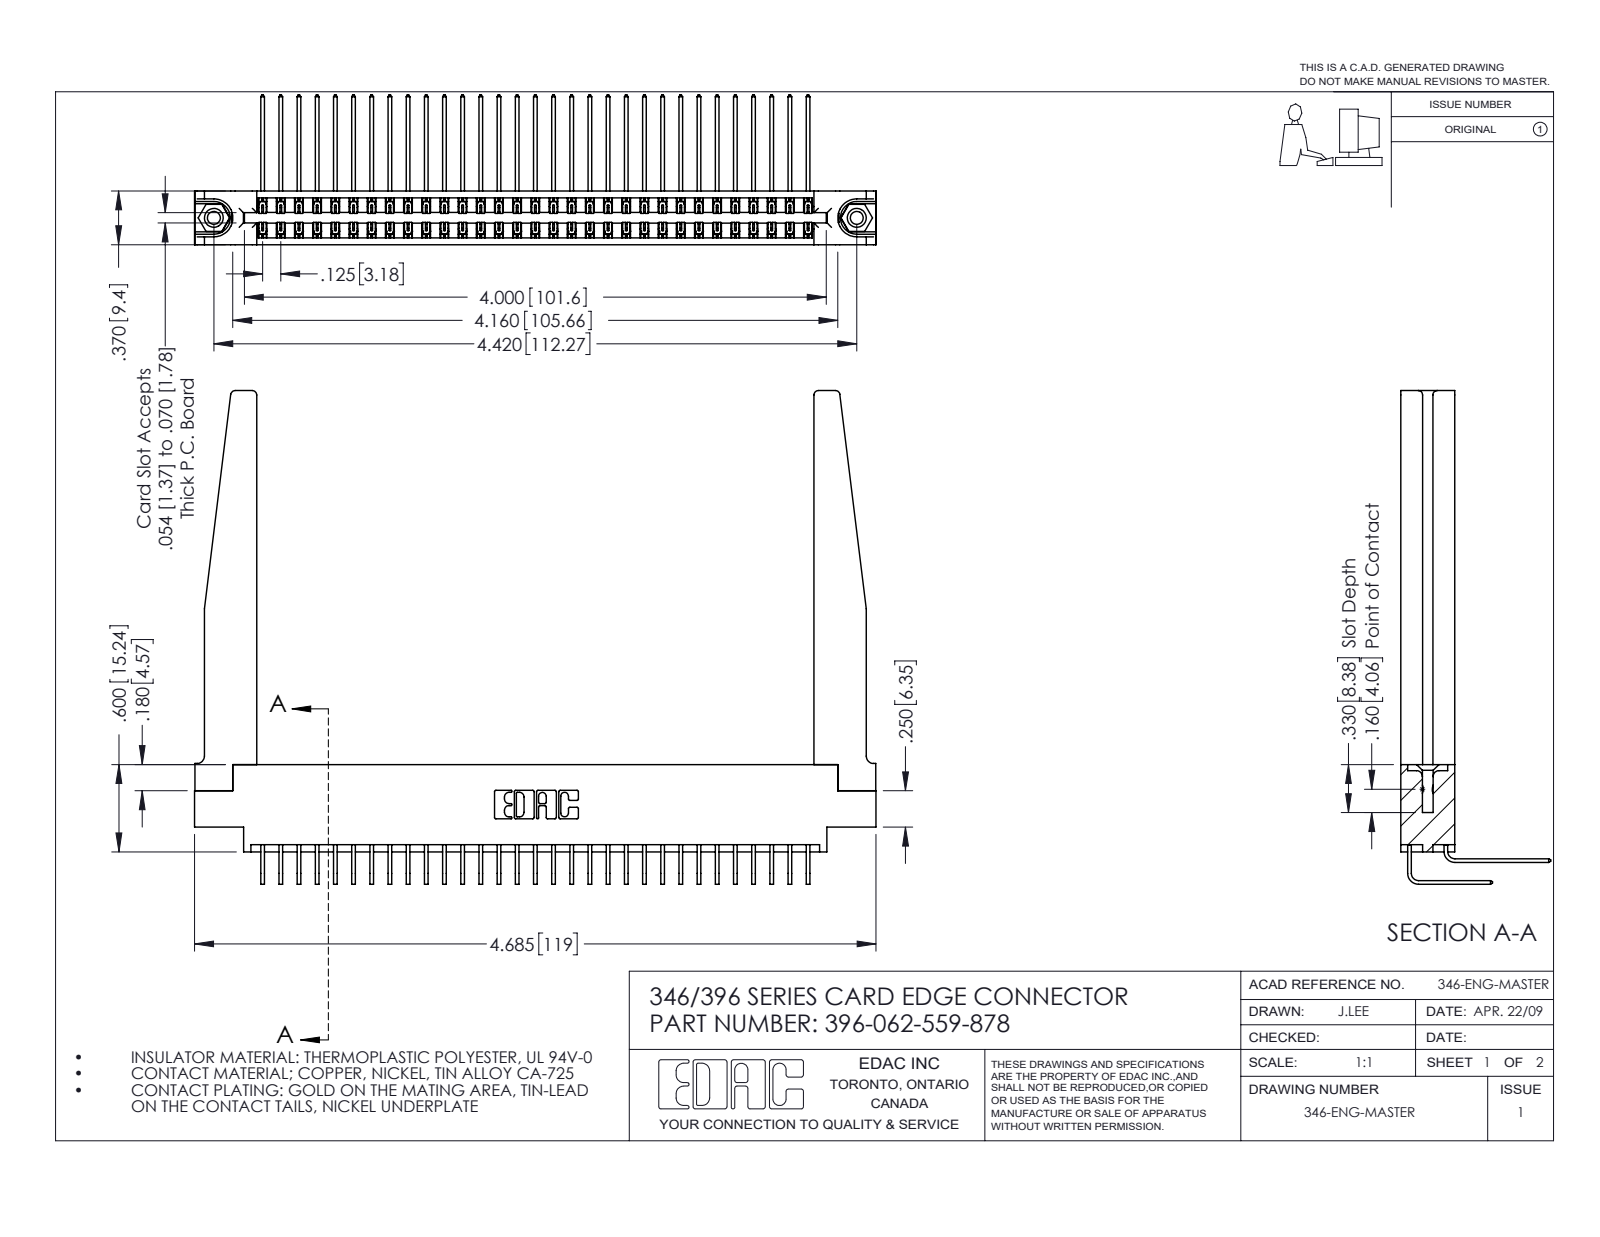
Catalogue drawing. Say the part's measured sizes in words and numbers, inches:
The part is named "345-292-001_559 Tail - 2; 396-062-559-878; 346-220-078_345-220-078; 346 Part_0.170 Offset - 0.156 Dia-TH (+2 more)". Its 3-D file was written by "SolidWorks 2016 (CONFIG_CONTROL_DESIGN)". It is 67 solids with 3708 faces: 2516 planar, 1140 cylindrical and 52 other. Overall it measures 4.685 by 3.393 by 1.03 inches. Its volume is 1.137 cubic inches and its surface area 37.78 square inches. Round holes: 2 of diameter 0.089, 2 of diameter 0.125, 2 of diameter 0.156, 1 of diameter 0.064. Round bosses or shafts: 2 of diameter 0.155. Partial cylindrical surfaces (rounded edges, fillets, slot ends): 93 of radius 0.006, 22 of radius 0.01, 8 of radius 0.03, 6 of radius 0.007, 6 of radius 0.031, 4 of radius 0.05, 3 of radius 0.026, 2 of radius 0.014. The main face-to-face distances are 0.37, 0.048, 0.322, 0.072, 0.025, 0.148, 0.15, 0.25, 0.298, 0.275. The hole center spacings are 0.246, 4.212, 4.42.
